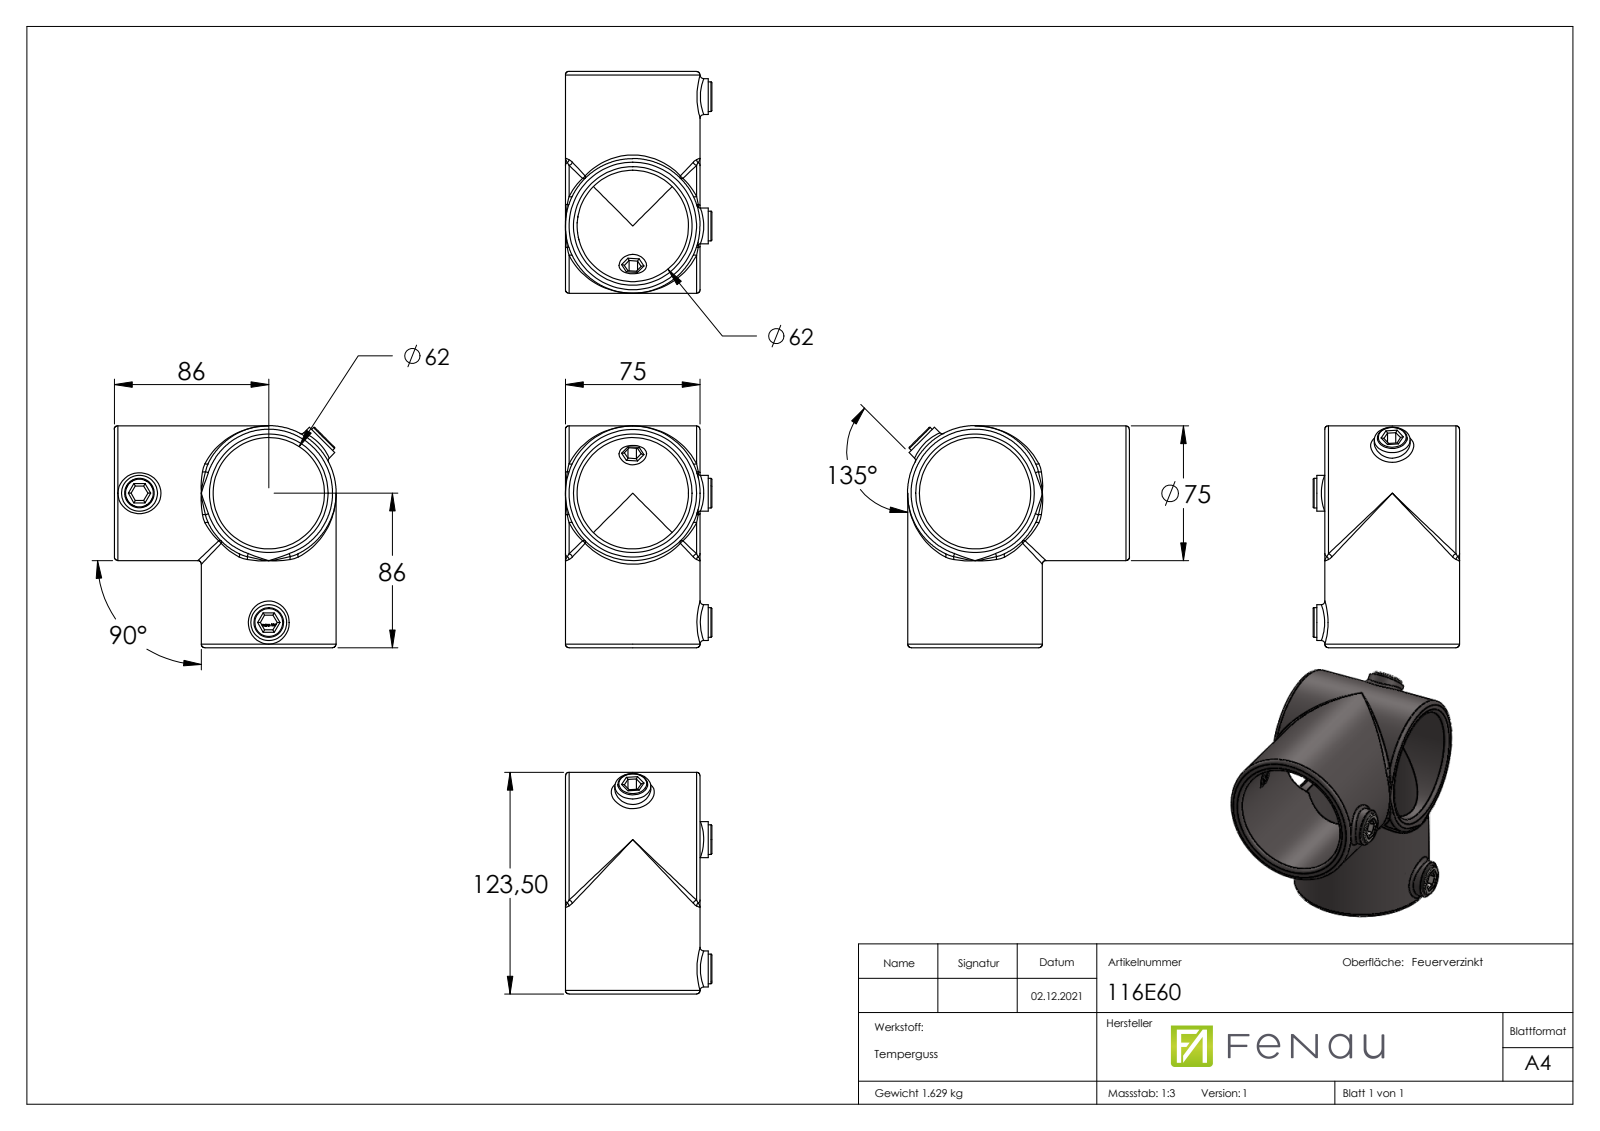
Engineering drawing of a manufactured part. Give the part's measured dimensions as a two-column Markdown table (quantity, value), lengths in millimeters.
| quantity | value |
| --- | --- |
| part name | 116-E60 Teil2; 116-E60; 116-E60 Teil1_116-E60 Teil1; 116-E60 Teil1 |
| STEP written by | SolidWorks 2018 (CONFIG_CONTROL_DESIGN) |
| units | millimeters |
| bodies | 4 solids, 363 faces (139 planar, 75 cylindrical, 149 other) |
| overall size | 123.5 × 123.5 × 81.5 |
| volume | 222 697 mm³ |
| surface area | 76 686 mm² |
| round holes (diameter × count) | 15.25 × 3, 62 × 3 |
| round bosses / shafts (diameter × count) | 20 × 3, 16.5 × 3, 75 × 2 |
| partial cylindrical surfaces (radius × count) | 2 × 36, 31.1 × 2, 37.5 × 1 |
| main face-to-face distances | 75, 6.5, 8.1, 2, 79.5, 4.5, 81.5, 68.5, 11, 13 |
| hole center spacings | 72, 101.82 |
